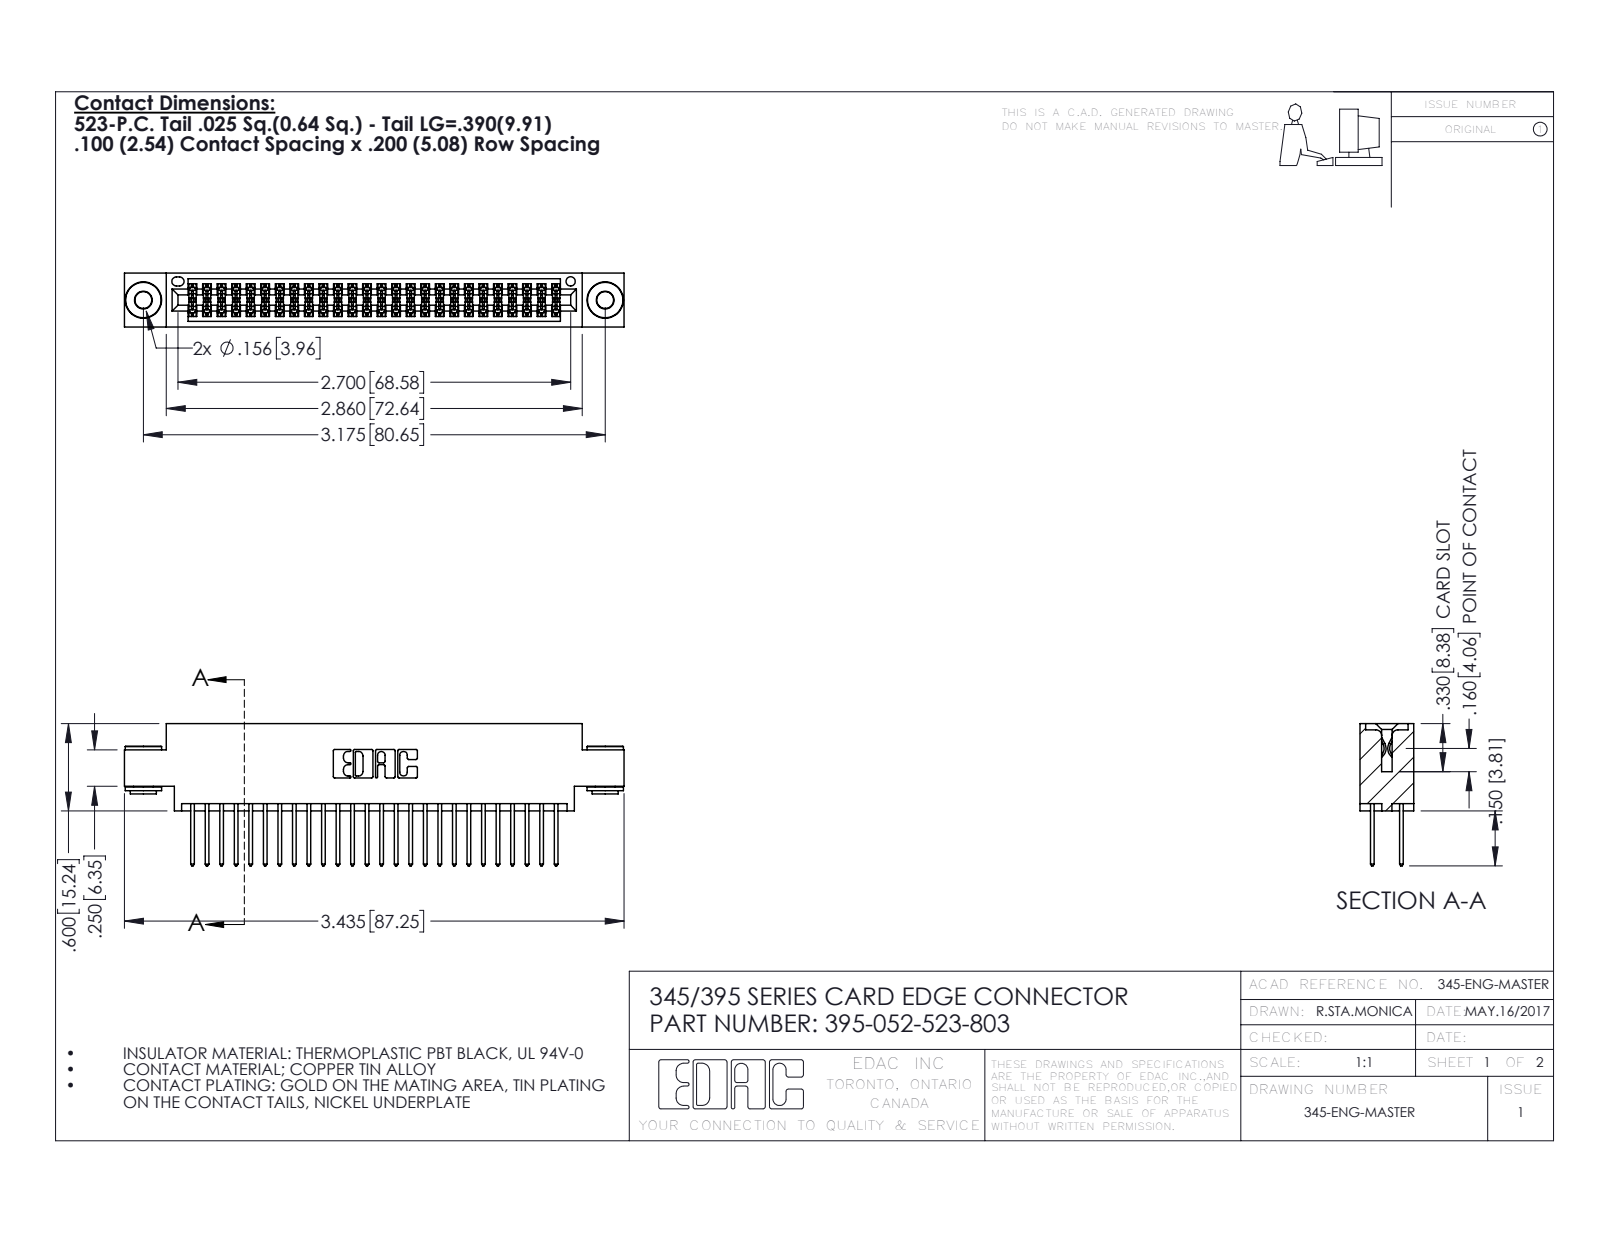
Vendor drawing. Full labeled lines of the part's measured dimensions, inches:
Part name (STEP PRODUCT): 395-052-523-803; 345-250-002_345-250-002-102; 345-292-001_345-293-123; 345 Part_0.170 Offset - 0.156 Dia-TH
STEP written by: SolidWorks 2016 (CONFIG_CONTROL_DESIGN)
Units: inches
Bodies: 55 solids, 2768 faces (1810 planar, 950 cylindrical, 8 other)
Overall size (bounding box): 3.435 × 0.977 × 0.37
Volume: 0.509 in³ · Surface area: 19.91 in²
Round holes (diameter × count): ⌀0.116 ×2, ⌀0.156 ×2, ⌀0.064 ×1
Round bosses / shafts (diameter × count): ⌀0.25 ×2, ⌀0.18 ×2, ⌀0.136 ×2
Partial cylindrical surfaces — rounded edges, fillets, slot ends (radius × count): R0.006 ×78, R0.01 ×52, R0.01 ×22, R0.007 ×6, R0.031 ×6, R0.026 ×3, R0.014 ×2, R0.019 ×2
Main face-to-face distances: 0.072, 0.298, 0.2, 0.37, 0.098, 0.272, 0.025, 0.225, 0.175, 0.149
Hole centre spacings: 0.27, 2.94, 3.175
